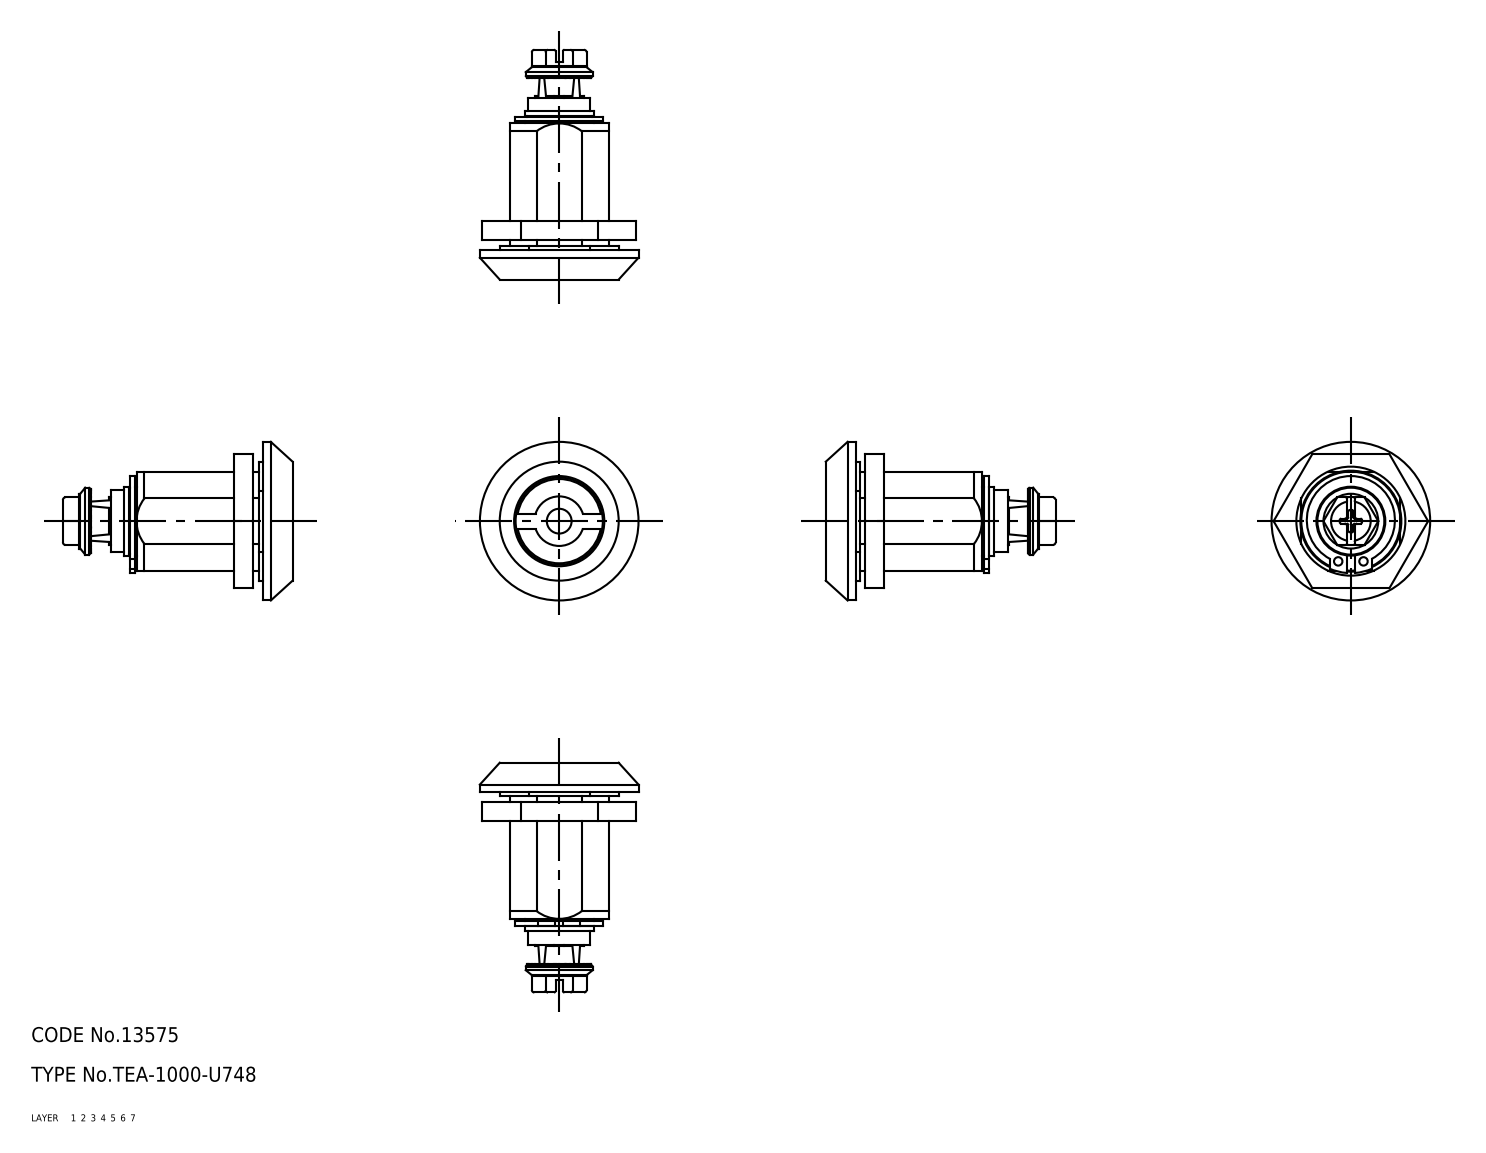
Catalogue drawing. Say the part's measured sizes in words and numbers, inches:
The part is named "67120358; 67120371; 67120384". Its 3-D file was written by "CADfix (AUTOMOTIVE_DESIGN)". It is 3 solids with 235 faces: 0 planar, 0 cylindrical and 235 other. Overall it measures 1.825 by 1.26 by 1.26 inches. Its volume is 0.92 cubic inches and its surface area 14.08 square inches.
